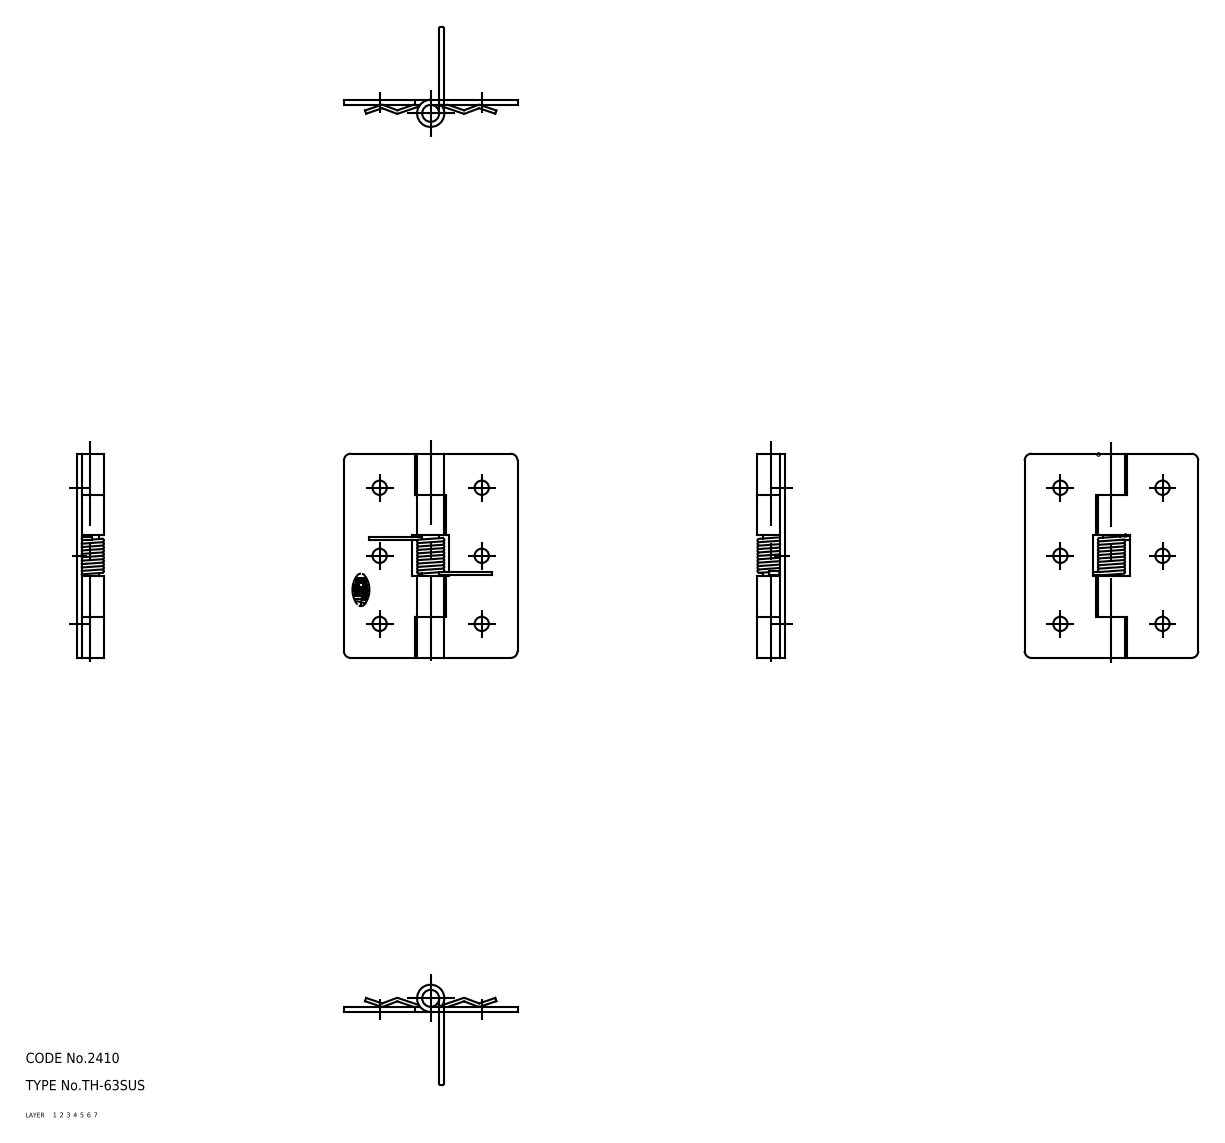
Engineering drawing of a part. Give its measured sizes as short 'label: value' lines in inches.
name: spring; shaft; hinge piece_B; hinge piece_A (+1 more)
written by: CADfix (AUTOMOTIVE_DESIGN)
unit: in
bodies: 4 solids, 86 faces (0 planar, 0 cylindrical, 86 other)
size: 2.362 × 2.008 × 0.315
volume: 0.402 in³; area: 14.88 in²
